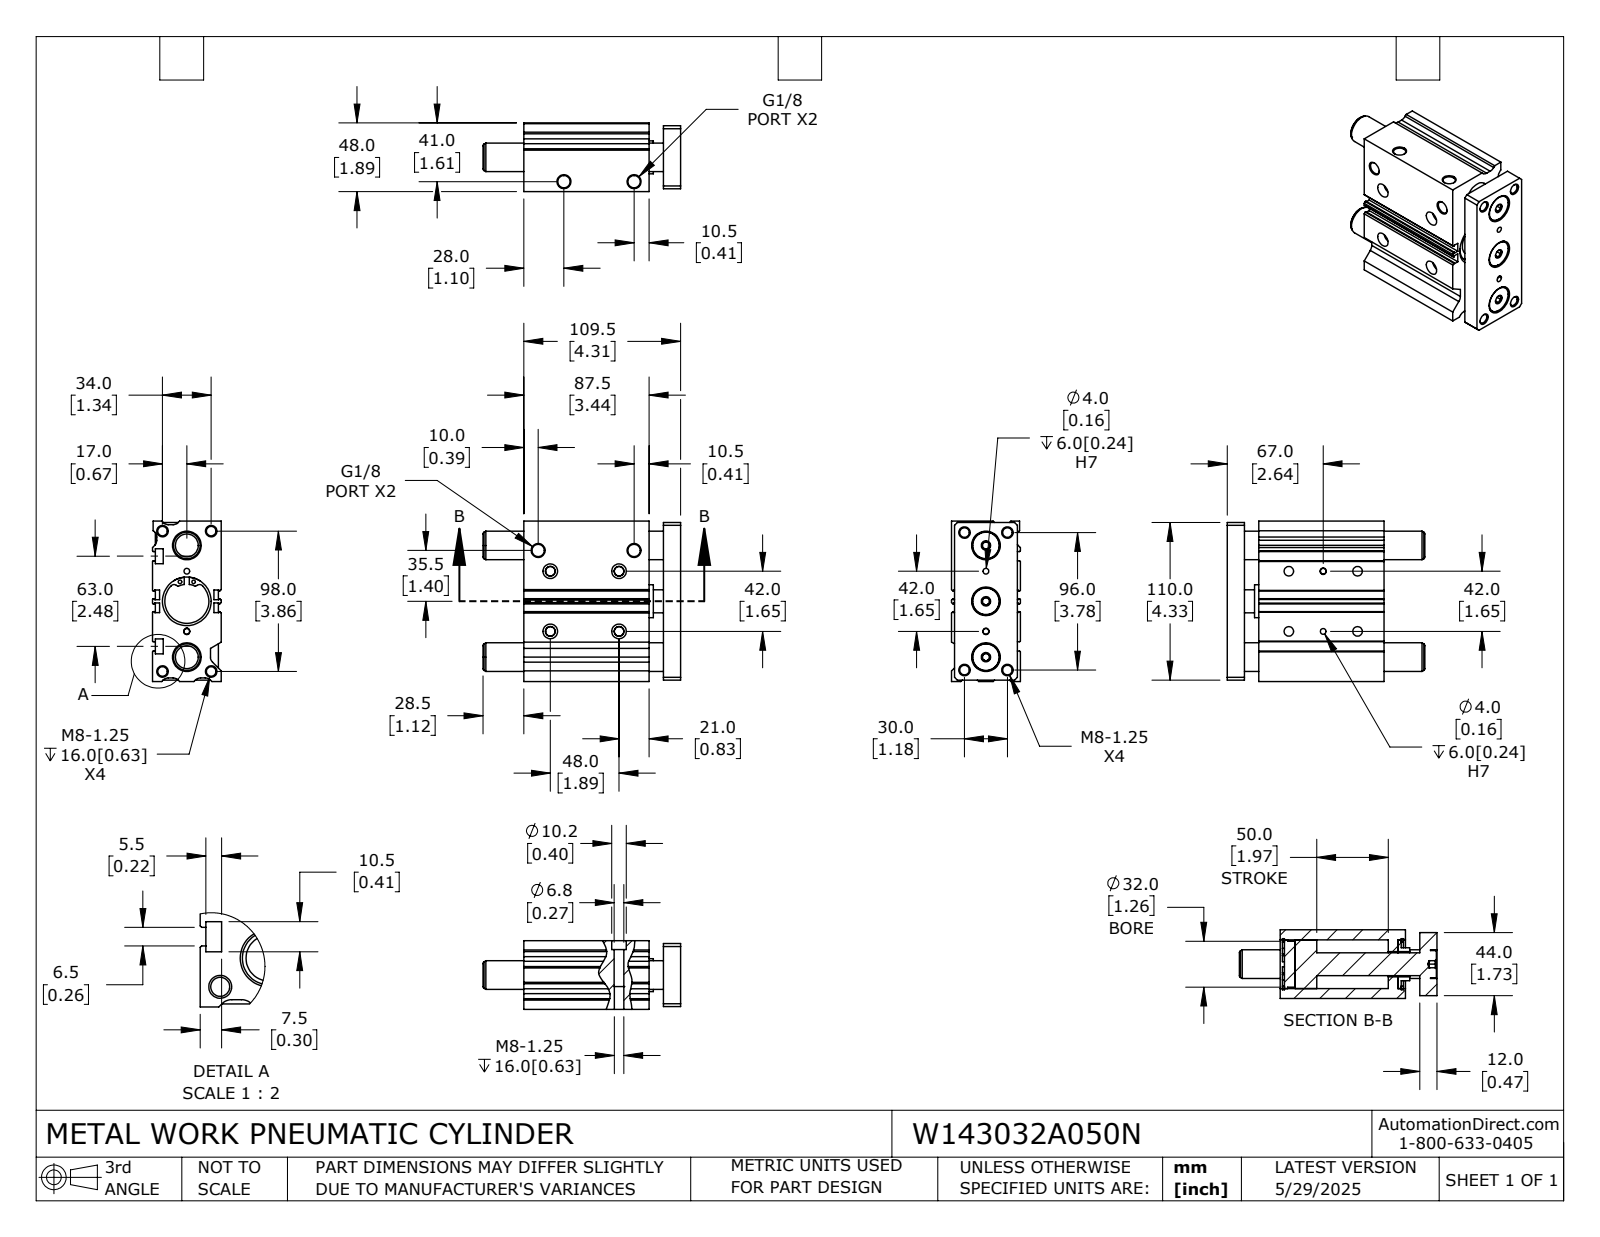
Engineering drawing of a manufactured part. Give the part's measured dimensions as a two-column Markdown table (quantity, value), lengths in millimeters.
| quantity | value |
| --- | --- |
| part name | W143032A050N_BODY; W143032A050N; W143032A050N_ROD |
| STEP written by | SolidWorks 2024 (CONFIG_CONTROL_DESIGN) |
| units | millimeters |
| bodies | 6 solids, 394 faces (195 planar, 149 cylindrical, 50 other) |
| overall size | 138 × 112 × 48 |
| volume | 458 000 mm³ |
| surface area | 117 000 mm² |
| round holes (diameter × count) | 6.7 × 12, 2.5 × 4, 4 × 4, 6.8 × 4, 8.6 × 4, 10.2 × 4, 5 × 3, 20 × 3, 17.7 × 1, 30.8 × 1 |
| round bosses / shafts (diameter × count) | 19 × 3, 35.7 × 2, 34 × 1, 32 × 1, 23 × 1, 16 × 1 |
| partial cylindrical surfaces (radius × count) | 5 × 9, 2 × 4, 3 × 4, 12.9 × 2 |
| main face-to-face distances | 48, 3, 12, 22, 109.5, 7.5, 2, 10, 87.5, 46 |
| hole center spacings | 2.2, 8.8, 14.4, 17.5, 19.7, 24, 25.9, 30.9 |
